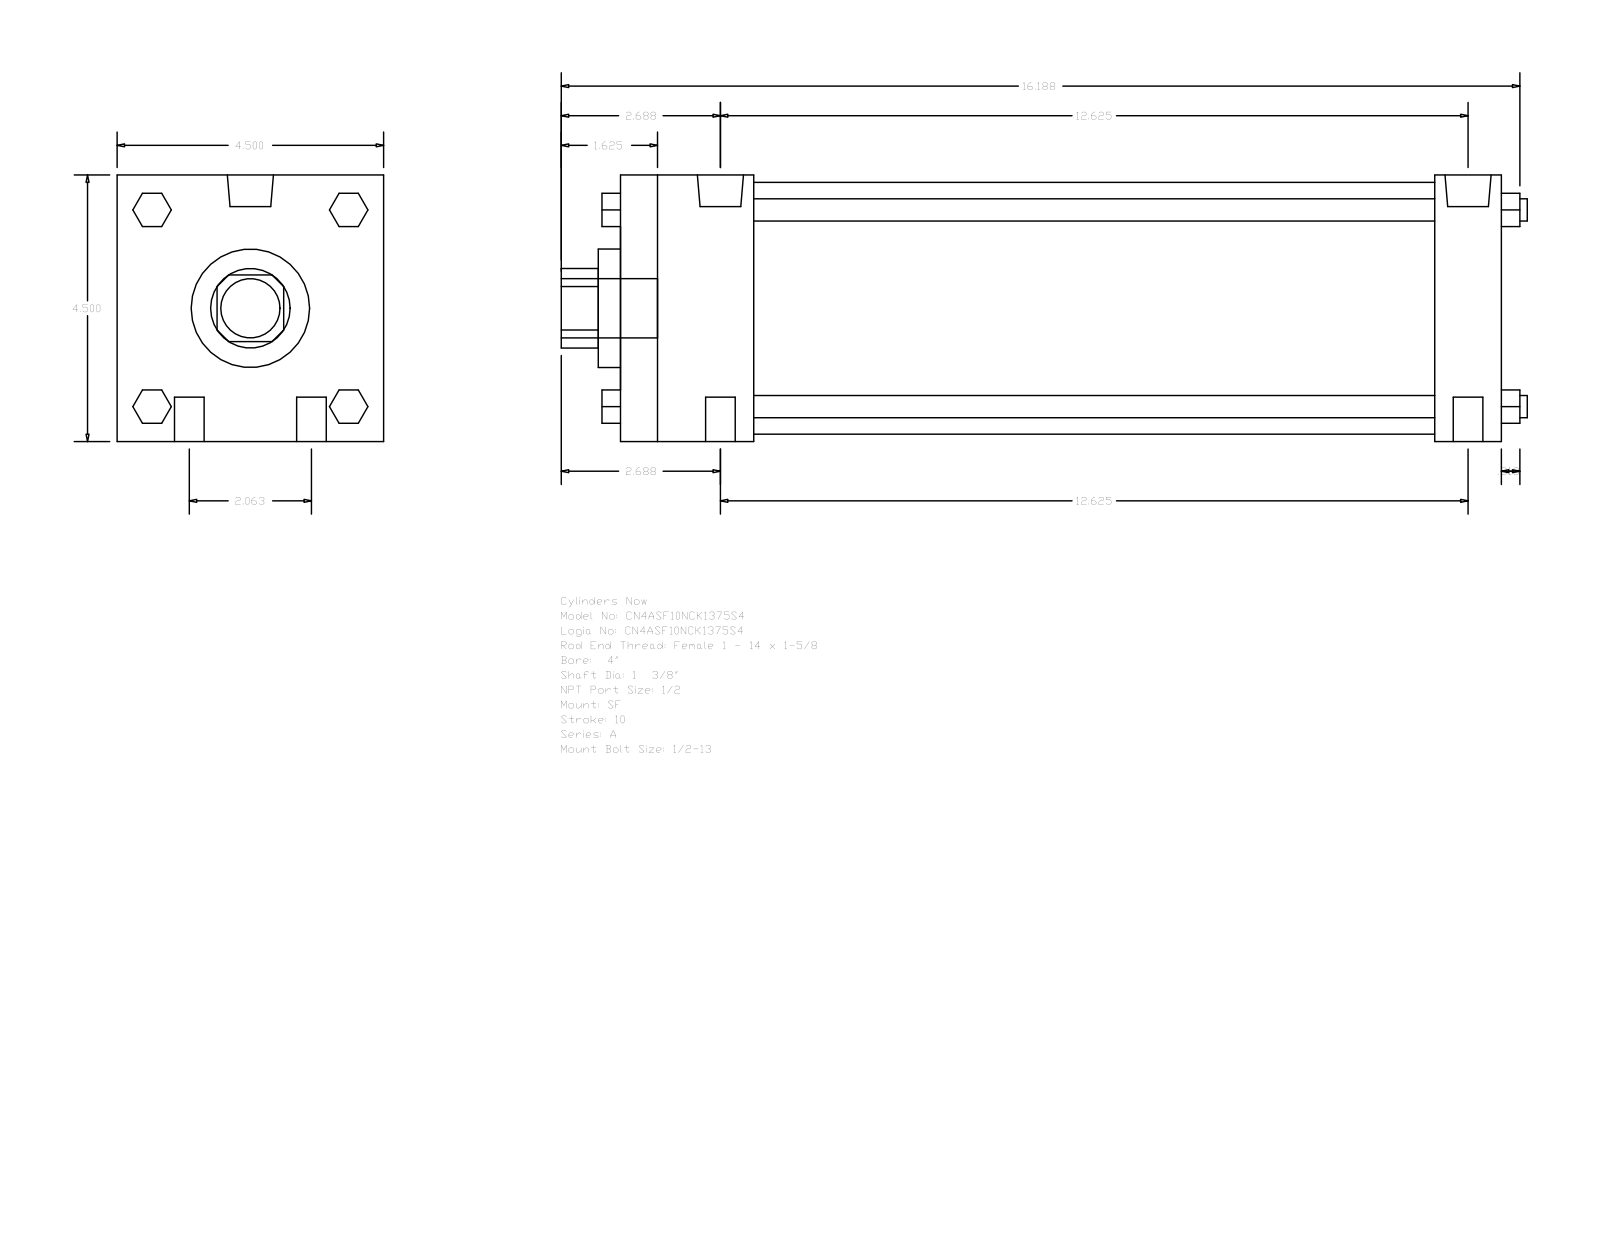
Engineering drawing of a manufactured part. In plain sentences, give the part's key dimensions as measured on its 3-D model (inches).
The part is named "A_SF__0400_1.375". Its 3-D file was written by "GSSL Pune (CONFIG_CONTROL_DESIGN)". It is 0 solids with 124 faces: 94 planar, 30 cylindrical and 0 other. Overall it measures 16.313 by 4.5 by 4.5 inches. Round holes: 1 of diameter 1.375, 1 of diameter 2, 1 of diameter 4.25. Round bosses or shafts: 4 of diameter 0.5, 4 of diameter 0.375, 2 of diameter 0.778, 2 of diameter 0.344, 1 of diameter 1. Partial cylindrical surfaces (rounded edges, fillets, slot ends): 1 of radius 0.672. The main face-to-face distances are 4.5, 14.875, 1.125, 13.75, 2.25, 11.5, 12.625, 0.563, 0.375, 2.625.
